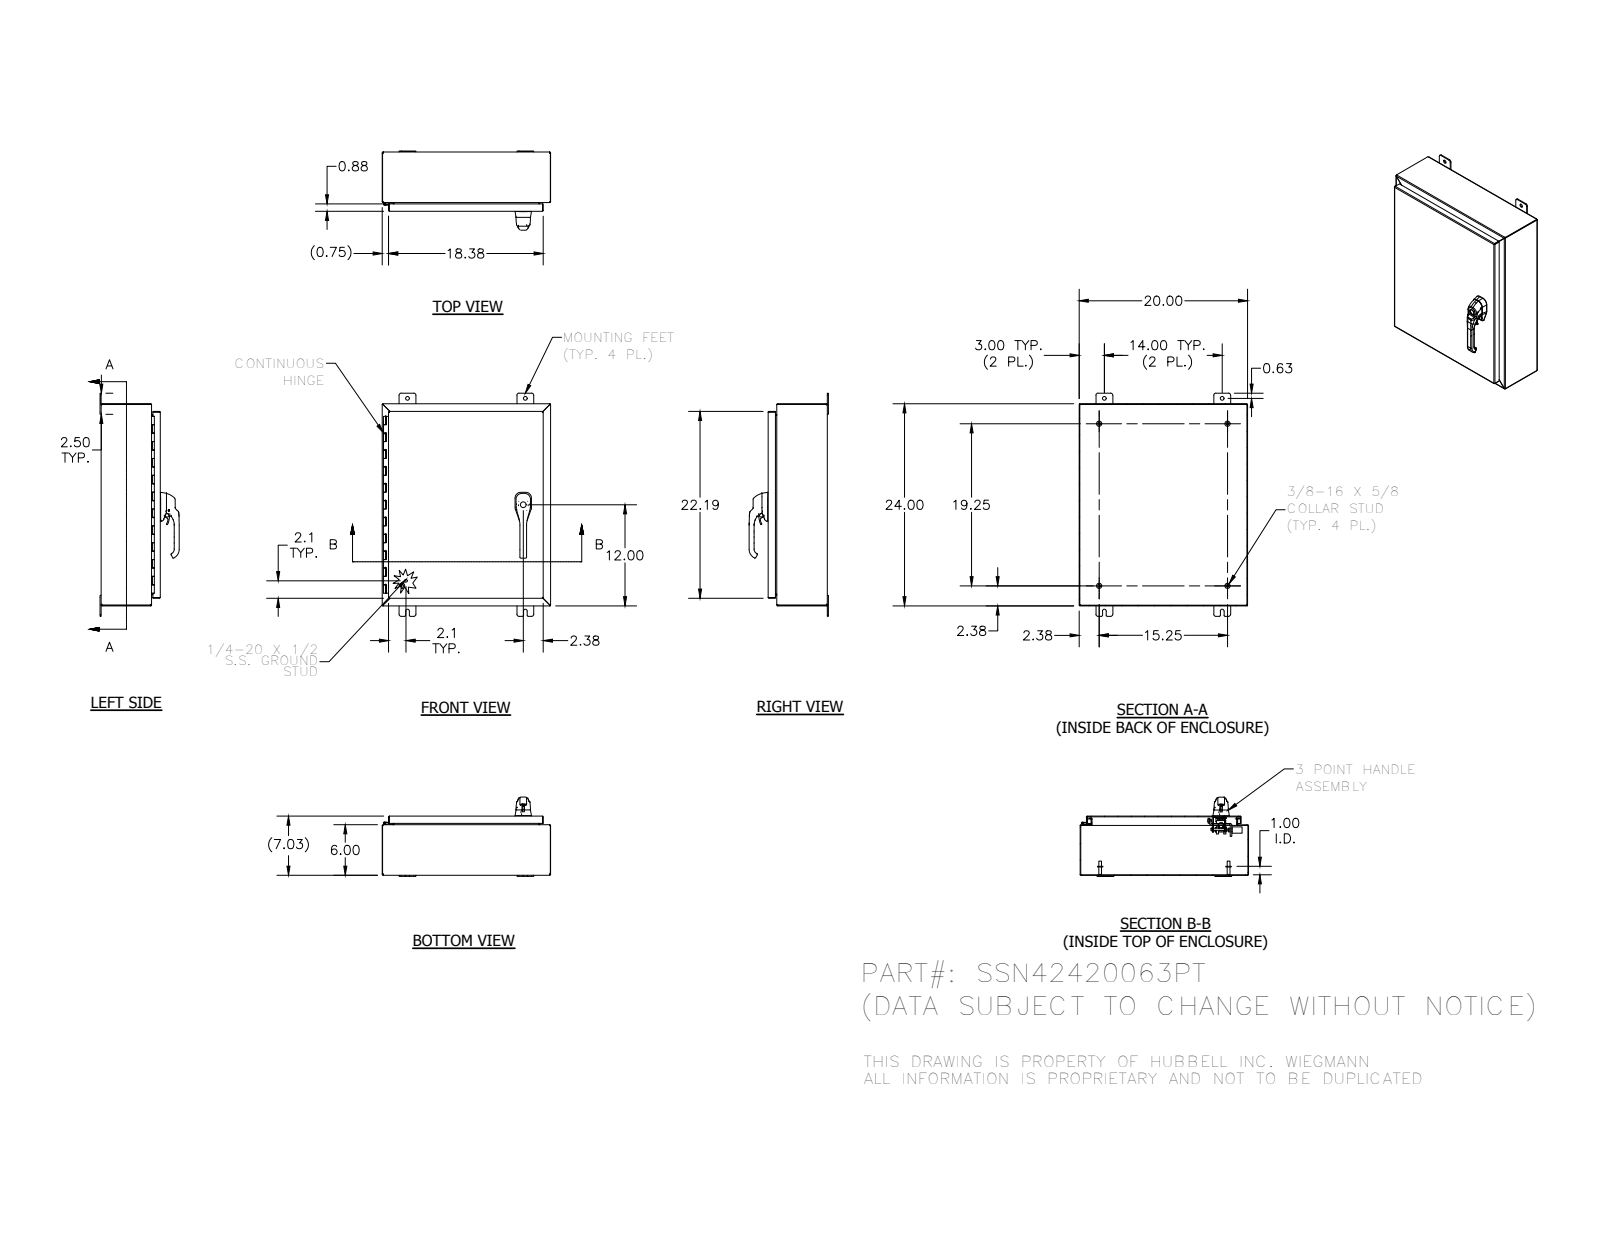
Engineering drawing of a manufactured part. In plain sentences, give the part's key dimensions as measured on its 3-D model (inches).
The part is named "1000-02; 1000-277-01; DIN985_M10; PLASTIC-ROLLER-CAM_AF0_ASM (+8 more)". Its 3-D file was written by "SolidWorks 2014 (AUTOMOTIVE_DESIGN)". It is 56 solids with 3059 faces: 1014 planar, 1260 cylindrical and 785 other. Overall it measures 26.5 by 20 by 9.408 inches. Its volume is 150.2 cubic inches and its surface area 3 822 square inches. Round holes: 8 of diameter 0.262, 4 of diameter 0.187, 4 of diameter 0.438, 3 of diameter 0.213, 3 of diameter 0.281, 2 of diameter 0.241, 2 of diameter 0.25, 2 of diameter 0.252, 2 of diameter 0.315, 2 of diameter 0.4, 2 of diameter 0.402, 2 of diameter 0.413. Round bosses or shafts: 4 of diameter 0.625, 4 of diameter 0.33, 3 of diameter 0.236, 2 of diameter 1, 2 of diameter 0.563, 2 of diameter 0.533, 2 of diameter 0.531, 2 of diameter 0.5. Partial cylindrical surfaces (rounded edges, fillets, slot ends): 172 of radius 0.02, 113 of radius 0.012, 26 of radius 0.125, 24 of radius 0.031, 21 of radius 0.019, 20 of radius 0.105, 20 of radius 0.25, 16 of radius 0.025. The main face-to-face distances are 0.074, 6.959, 6.885, 7.033, 19.926, 23.926, 5.926, 1.033, 19.852, 20. The hole center spacings are 0.38, 0.492, 0.76, 0.886, 14.428, 0.234, 0.258, 0.38.
